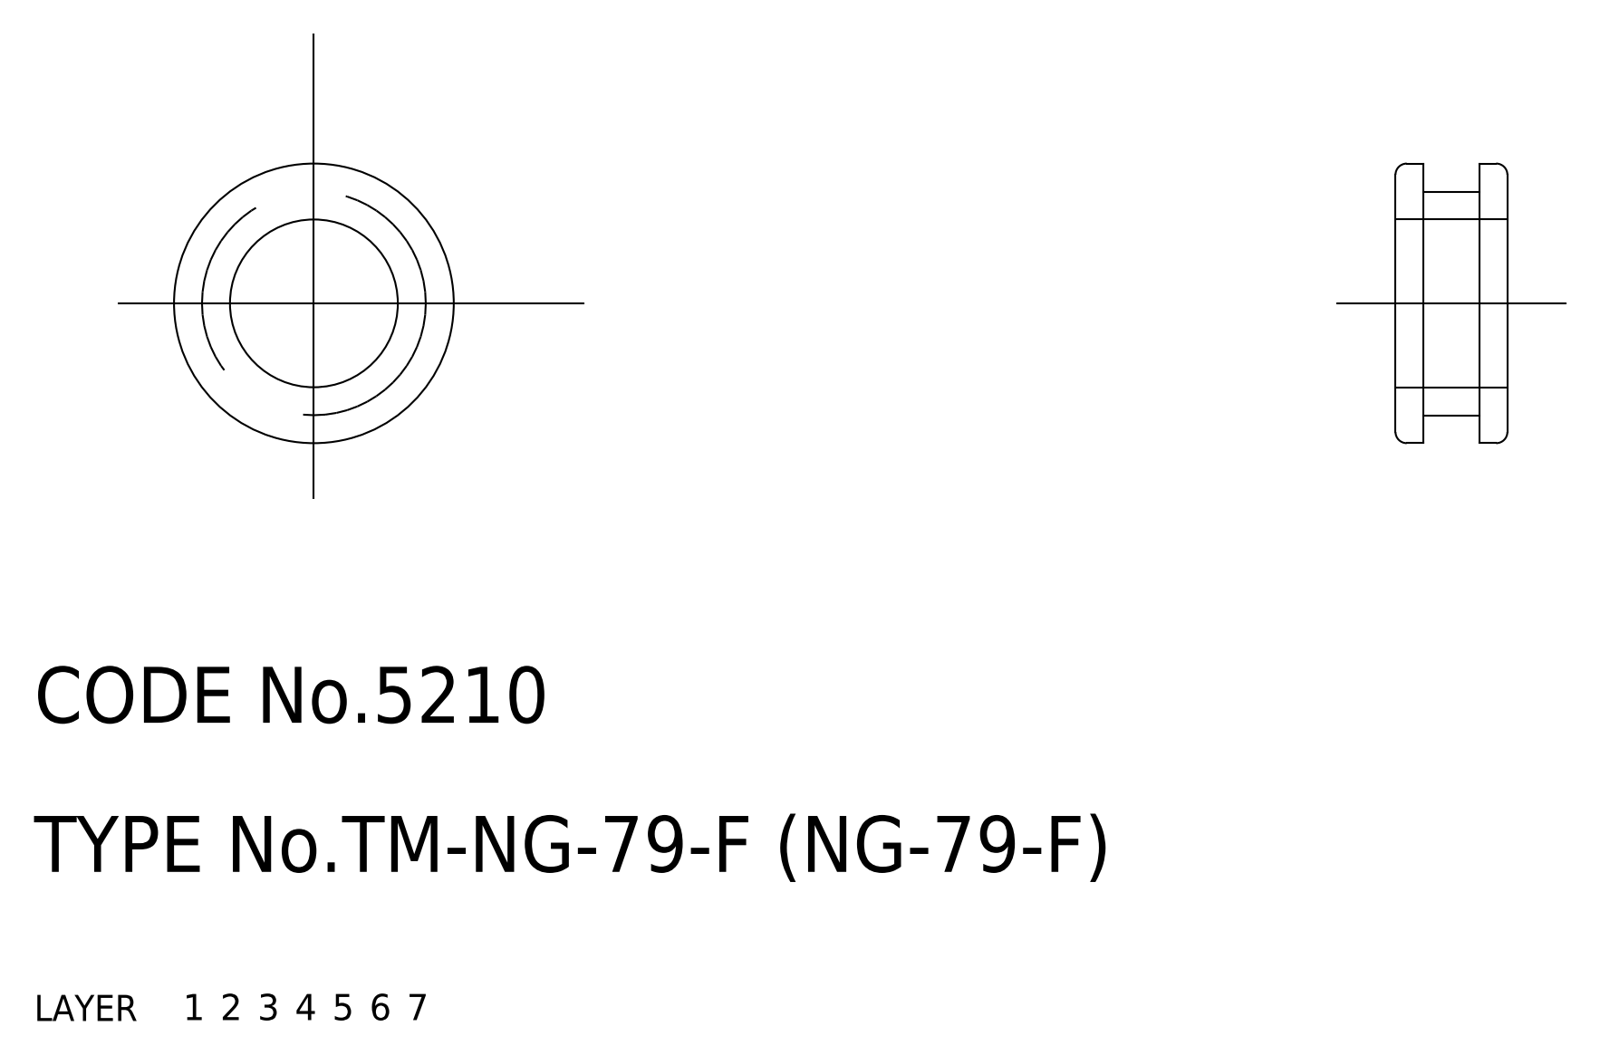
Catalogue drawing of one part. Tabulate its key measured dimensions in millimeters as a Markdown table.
| quantity | value |
| --- | --- |
| part name | grommet |
| STEP written by | CADfix (AUTOMOTIVE_DESIGN) |
| units | millimeters |
| bodies | 1 solid, 16 faces (0 planar, 0 cylindrical, 16 other) |
| overall size | 15 × 15 × 6 |
| volume | 482 mm³ |
| surface area | 753 mm² |
